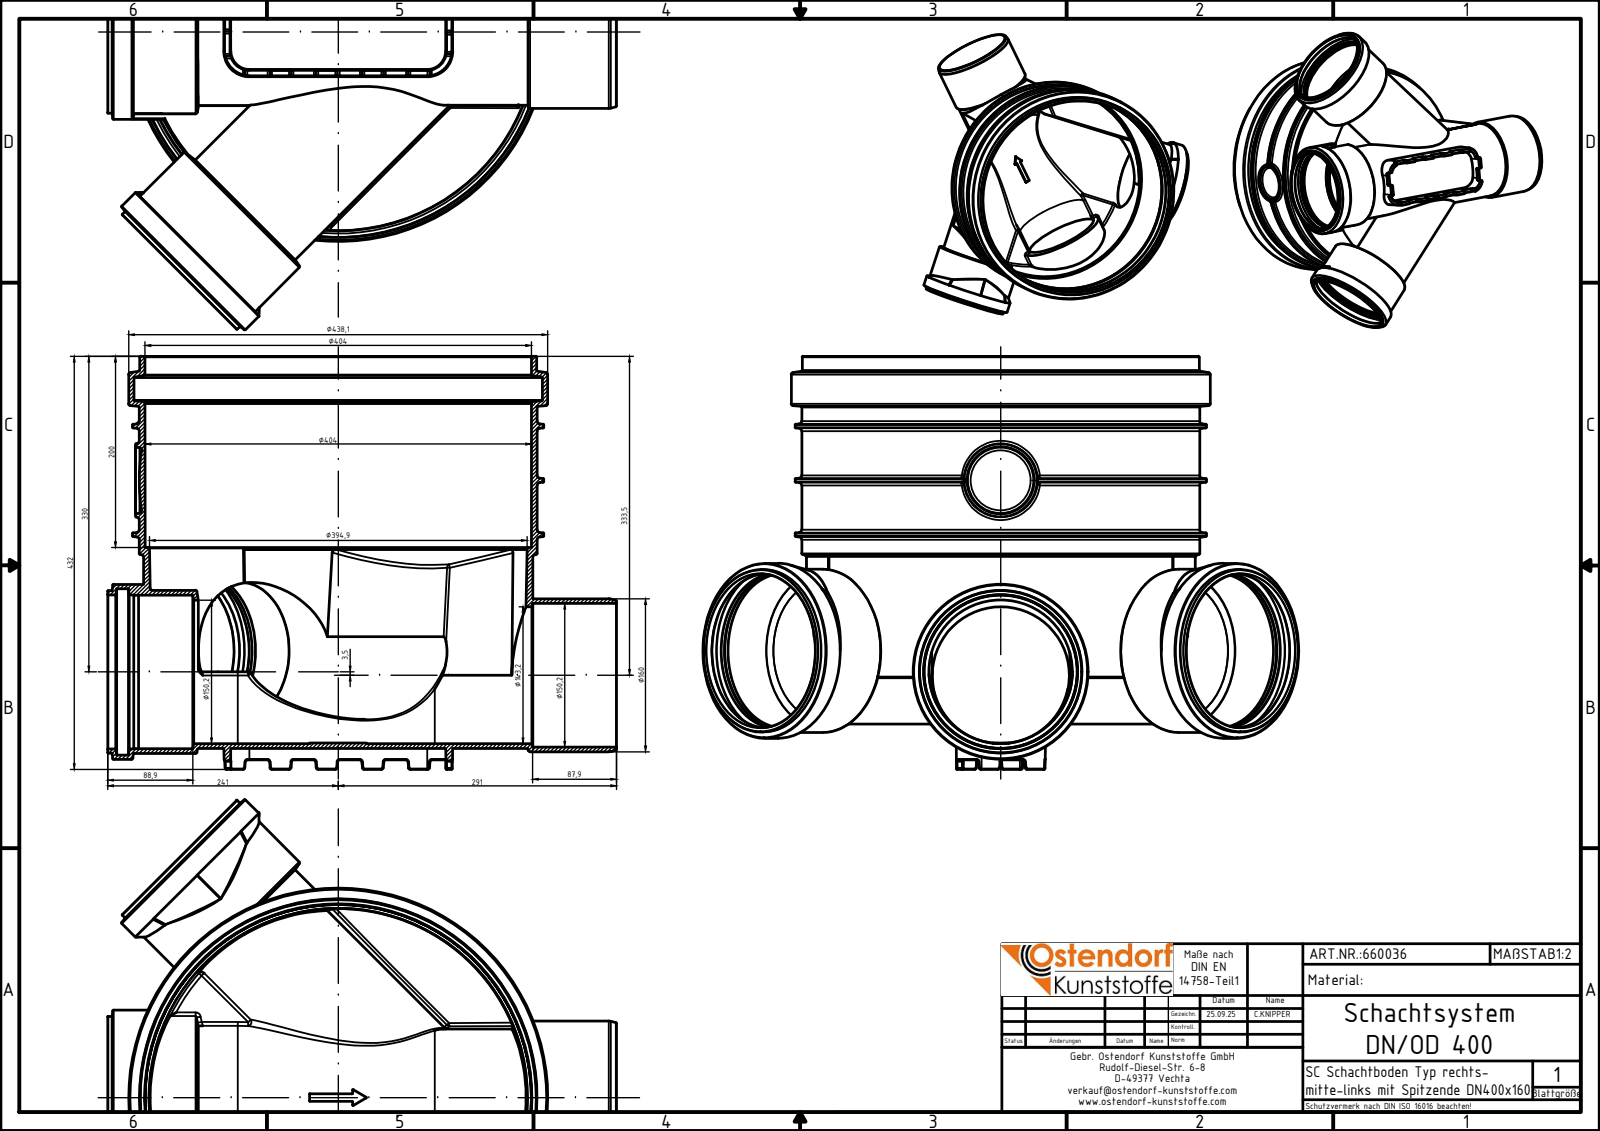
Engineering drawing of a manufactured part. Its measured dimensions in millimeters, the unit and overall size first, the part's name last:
Units: millimetres
Overall size (bounding box): 622.98 × 532 × 432
Round holes (diameter × count): ⌀160.8 ×5, ⌀143.2 ×3, ⌀173.8 ×3, ⌀150.2 ×2, ⌀160.9 ×2, ⌀160.5 ×1, ⌀404 ×1, ⌀404.4 ×1, ⌀427.1 ×1
Round bosses / shafts (diameter × count): ⌀182.8 ×3, ⌀170.6 ×3, ⌀169.8 ×3, ⌀438.1 ×1, ⌀430 ×1, ⌀416 ×1, ⌀415 ×1, ⌀160 ×1
Partial cylindrical surfaces — rounded edges, fillets, slot ends (radius × count): R1 ×56, R2 ×48, R4 ×8, R0.5 ×7, R76.5 ×2, R85.34 ×1, R203.44 ×1
Main face-to-face distances: 85.99, 336, 136, 200, 6, 130, 330, 231.99, 86, 92
Hole centre spacings: 3.5
Volume: 4 608 000 mm³ · Surface area: 1 671 000 mm²
Bodies: 1 solid, 689 faces (95 planar, 198 cylindrical, 396 other)
Part name (STEP PRODUCT): 660036z
STEP written by: Autodesk Inventor 2024 (AUTOMOTIVE_DESIGN)
